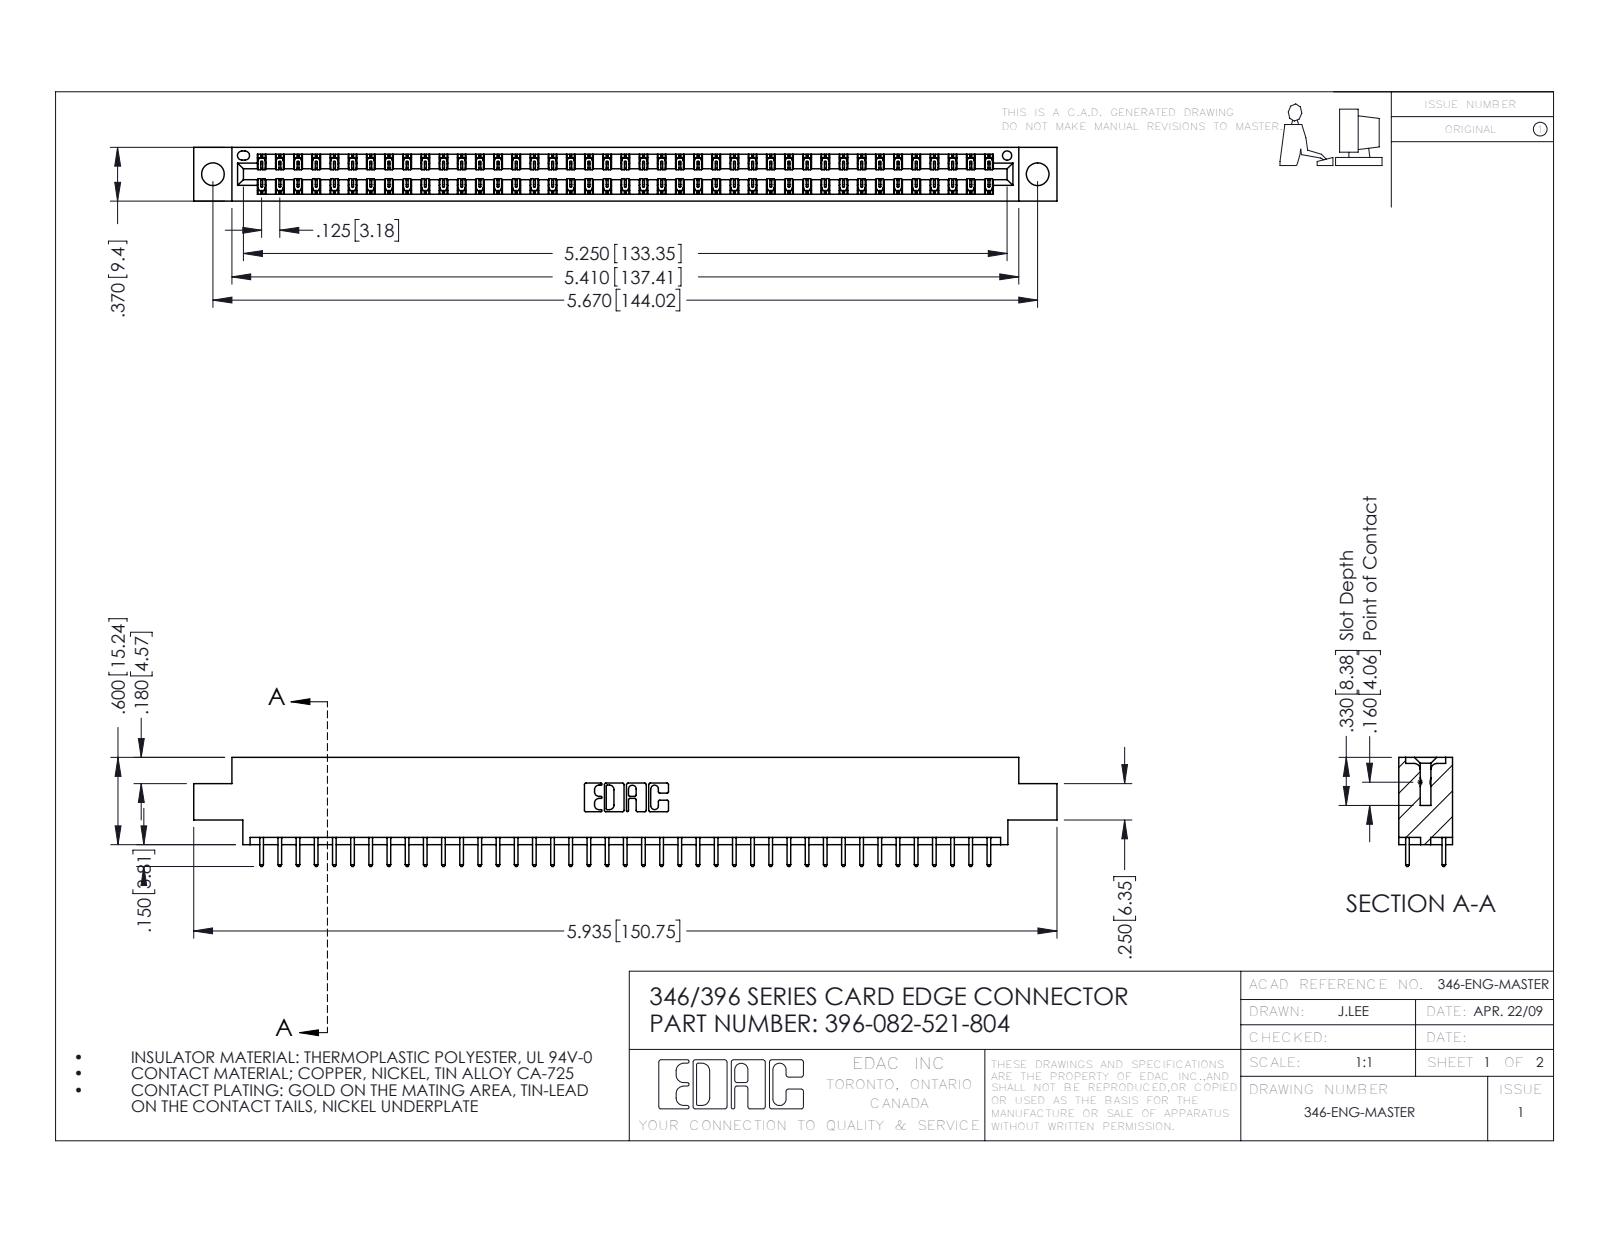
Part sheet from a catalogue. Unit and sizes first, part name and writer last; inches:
Units: inches
Overall size (bounding box): 5.935 × 0.75 × 0.37
Round holes (diameter × count): ⌀0.156 ×2, ⌀0.064 ×1
Partial cylindrical surfaces — rounded edges, fillets, slot ends (radius × count): R0.006 ×123, R0.01 ×82, R0.01 ×22, R0.007 ×6, R0.031 ×6, R0.026 ×3, R0.014 ×2, R0.022 ×2
Main face-to-face distances: 0.048, 0.322, 0.37, 0.25, 0.072, 0.298, 0.025, 0.275, 0.148, 0.222
Hole centre spacings: 0.246, 5.461, 5.67
Volume: 0.88 in³ · Surface area: 30.33 in²
Bodies: 83 solids, 4390 faces (2950 planar, 1440 cylindrical, 0 other)
Part name (STEP PRODUCT): 396-082-521-804; 345-292-001_345-293-121; 346 Part_0.170 Offset - 0.156 Dia-TH
STEP written by: SolidWorks 2016 (CONFIG_CONTROL_DESIGN)
